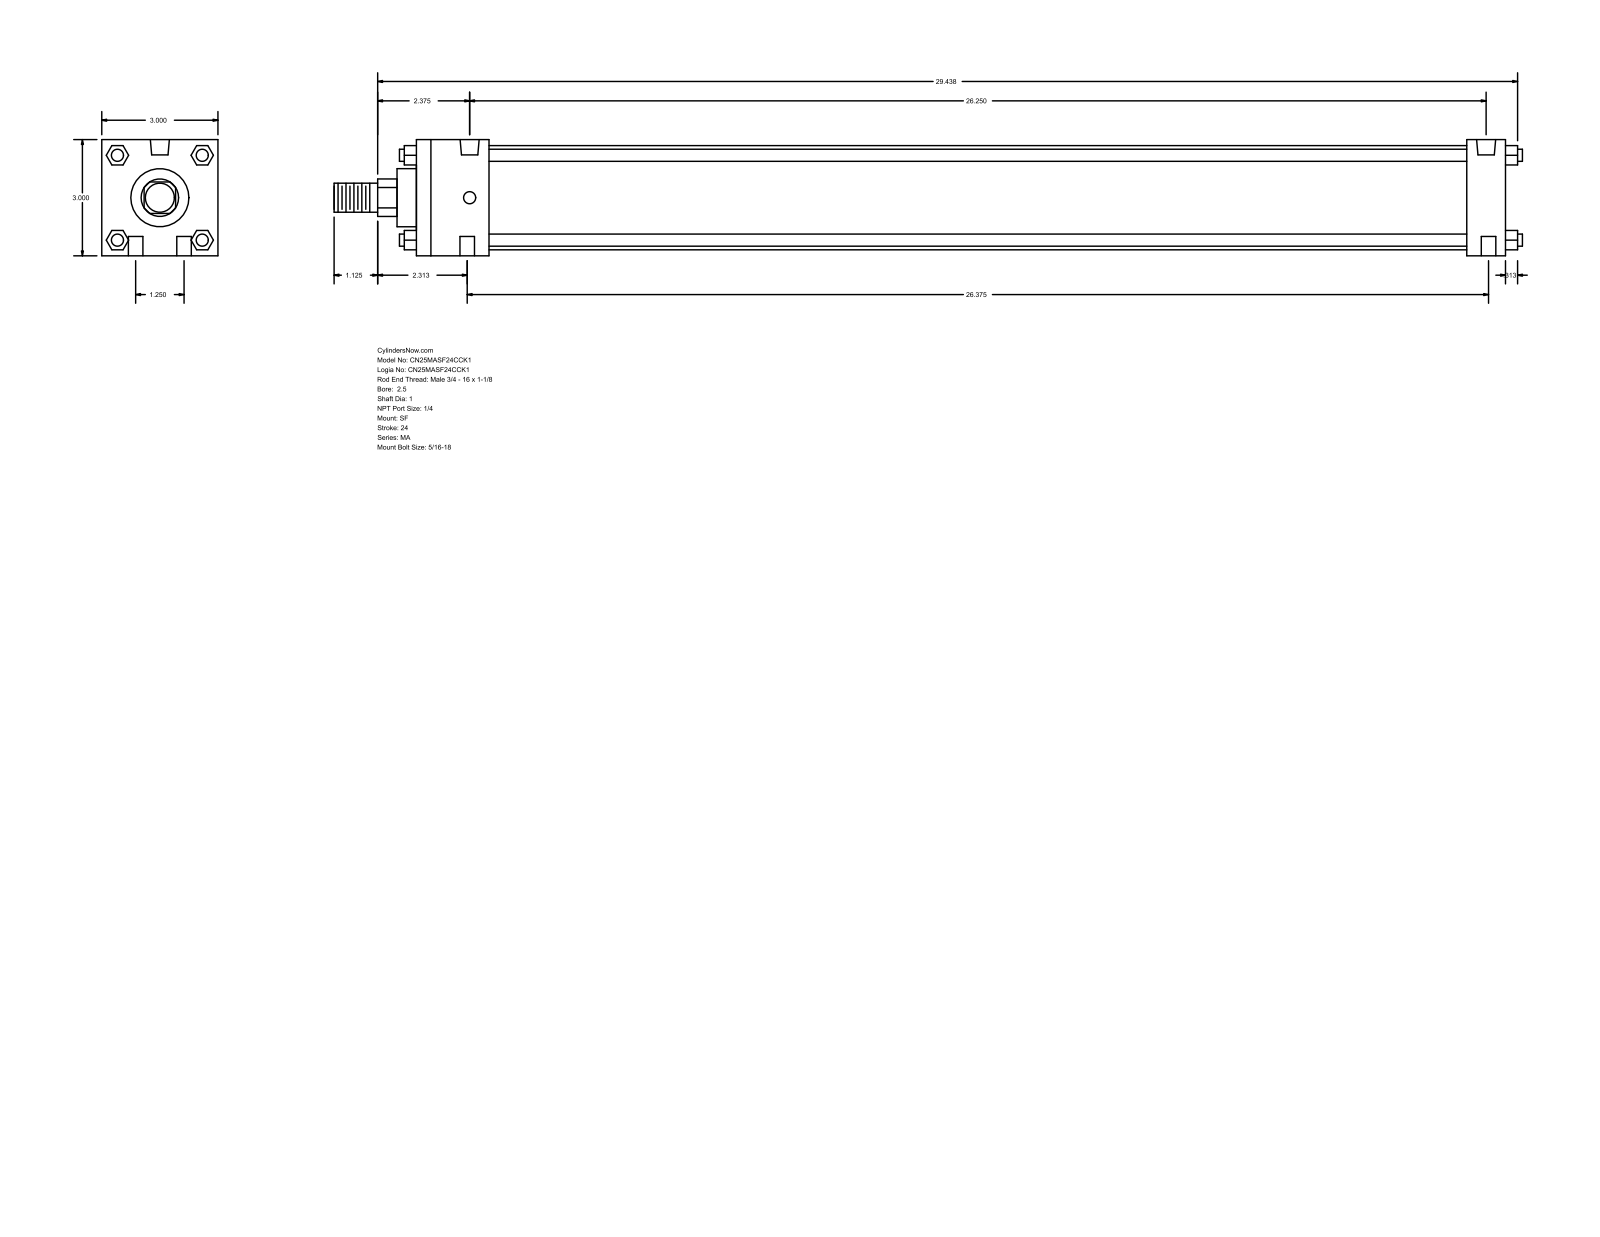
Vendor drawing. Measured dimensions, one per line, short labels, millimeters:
name: MA_SF__0250_1
written by: GSSL Pune (CONFIG_CONTROL_DESIGN)
unit: mm
bodies: 0 solids, 124 faces (94 planar, 30 cylindrical, 0 other)
size: 779.46 × 76.2 × 76.2
holes: 4× ⌀9.53, 2× ⌀7.94, 2× ⌀12.49
bosses: 4× ⌀7.94, 1× ⌀68.33, 1× ⌀38.1, 1× ⌀25.4, 1× ⌀19.05
rounds: 1× R12.29
face distances: 76.2, 714.37, 12.7, 688.98, 25.39, 47.63, 641.35, 666.74, 27.81, 48.17
hole spacings: 15.96, 31.76, 666.75, 668.52, 668.53, 669.92, 670.67
